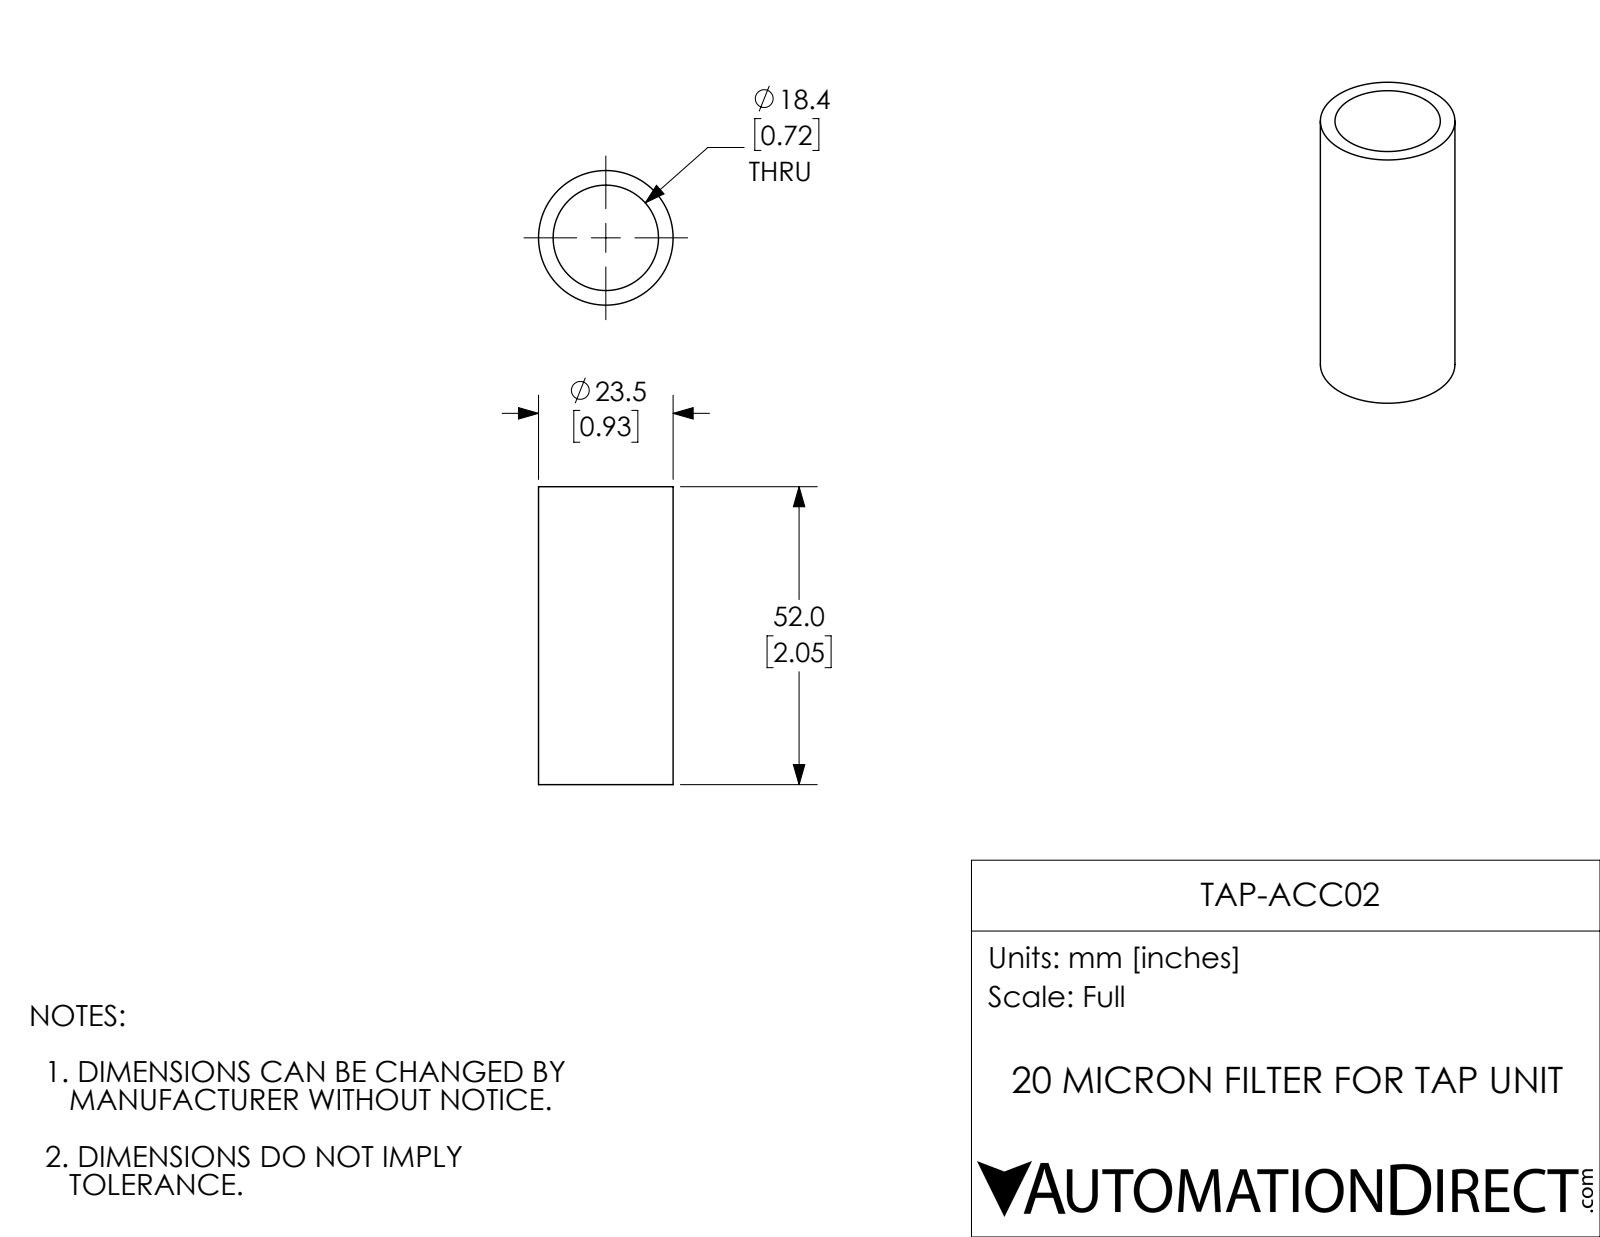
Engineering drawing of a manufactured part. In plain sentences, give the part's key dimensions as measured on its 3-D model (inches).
The part is named "TAP-ACC02". Its 3-D file was written by "SolidWorks 2017 (AUTOMOTIVE_DESIGN)". It is 1 solid with 6 faces: 2 planar, 4 cylindrical and 0 other. Overall it measures 2.047 by 0.925 by 0.925 inches. Its volume is 0.533 cubic inches and its surface area 11.13 square inches. Round holes: 1 of diameter 0.724. Round bosses or shafts: 1 of diameter 0.925. The main face-to-face distances are 2.047.
